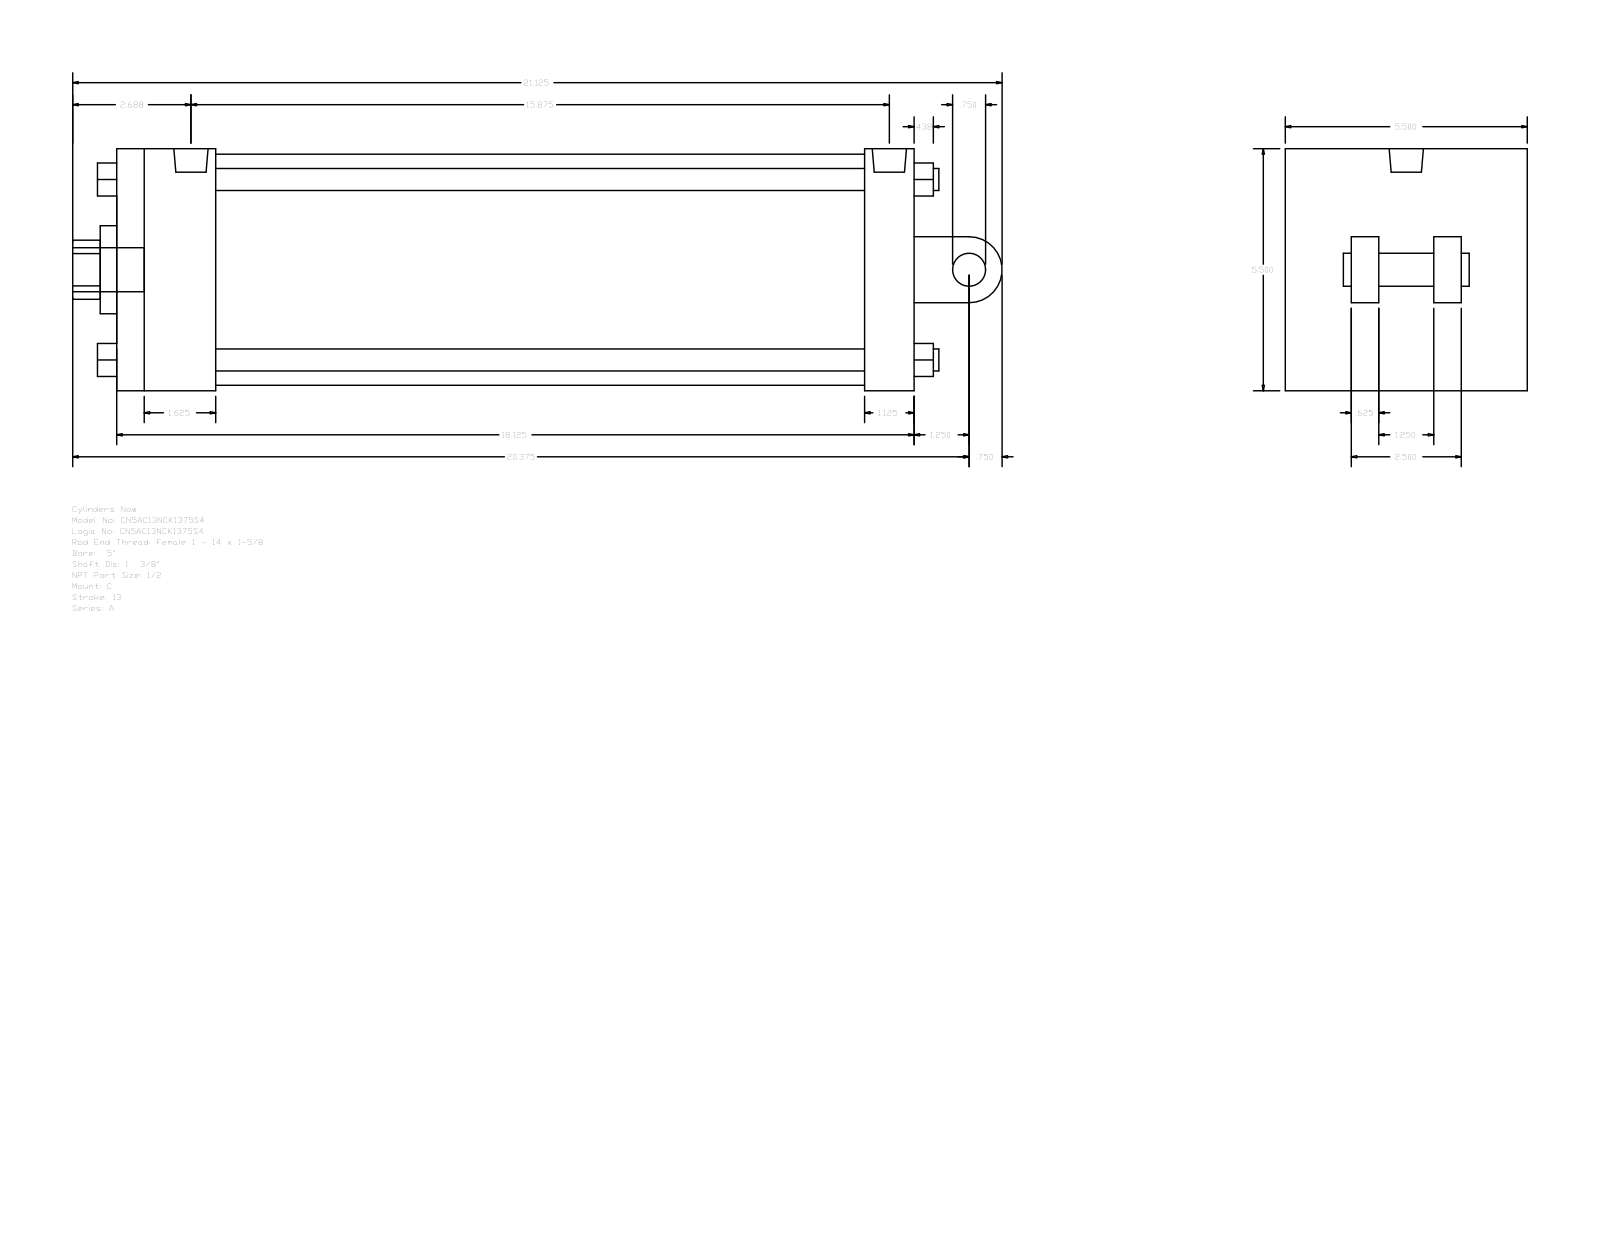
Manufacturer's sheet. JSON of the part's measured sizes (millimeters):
{"part_name": "A_C__0500_1.375", "step_written_by": "GSSL Pune (CONFIG_CONTROL_DESIGN)", "units": "millimeters", "bodies": {"solids": 0, "faces": 135, "planar": 102, "cylindrical": 33, "other": 0}, "overall_size": [536.58, 139.7, 139.7], "round_holes": [[8.73, 2], [19.77, 1], [34.92, 1], [50.8, 1], [133.35, 1]], "round_bosses_or_shafts": [[12.7, 4], [8.73, 2], [25.4, 1], [19.77, 1], [19.05, 1]], "partial_cylinders_radius": [[17.06, 1], [19.05, 1]], "face_to_face_distances": [139.7, 460.37, 28.57, 57.15, 431.8, 374.65, 403.22, 38.1, 15.87, 101.6], "hole_center_spacings": [2.39]}
